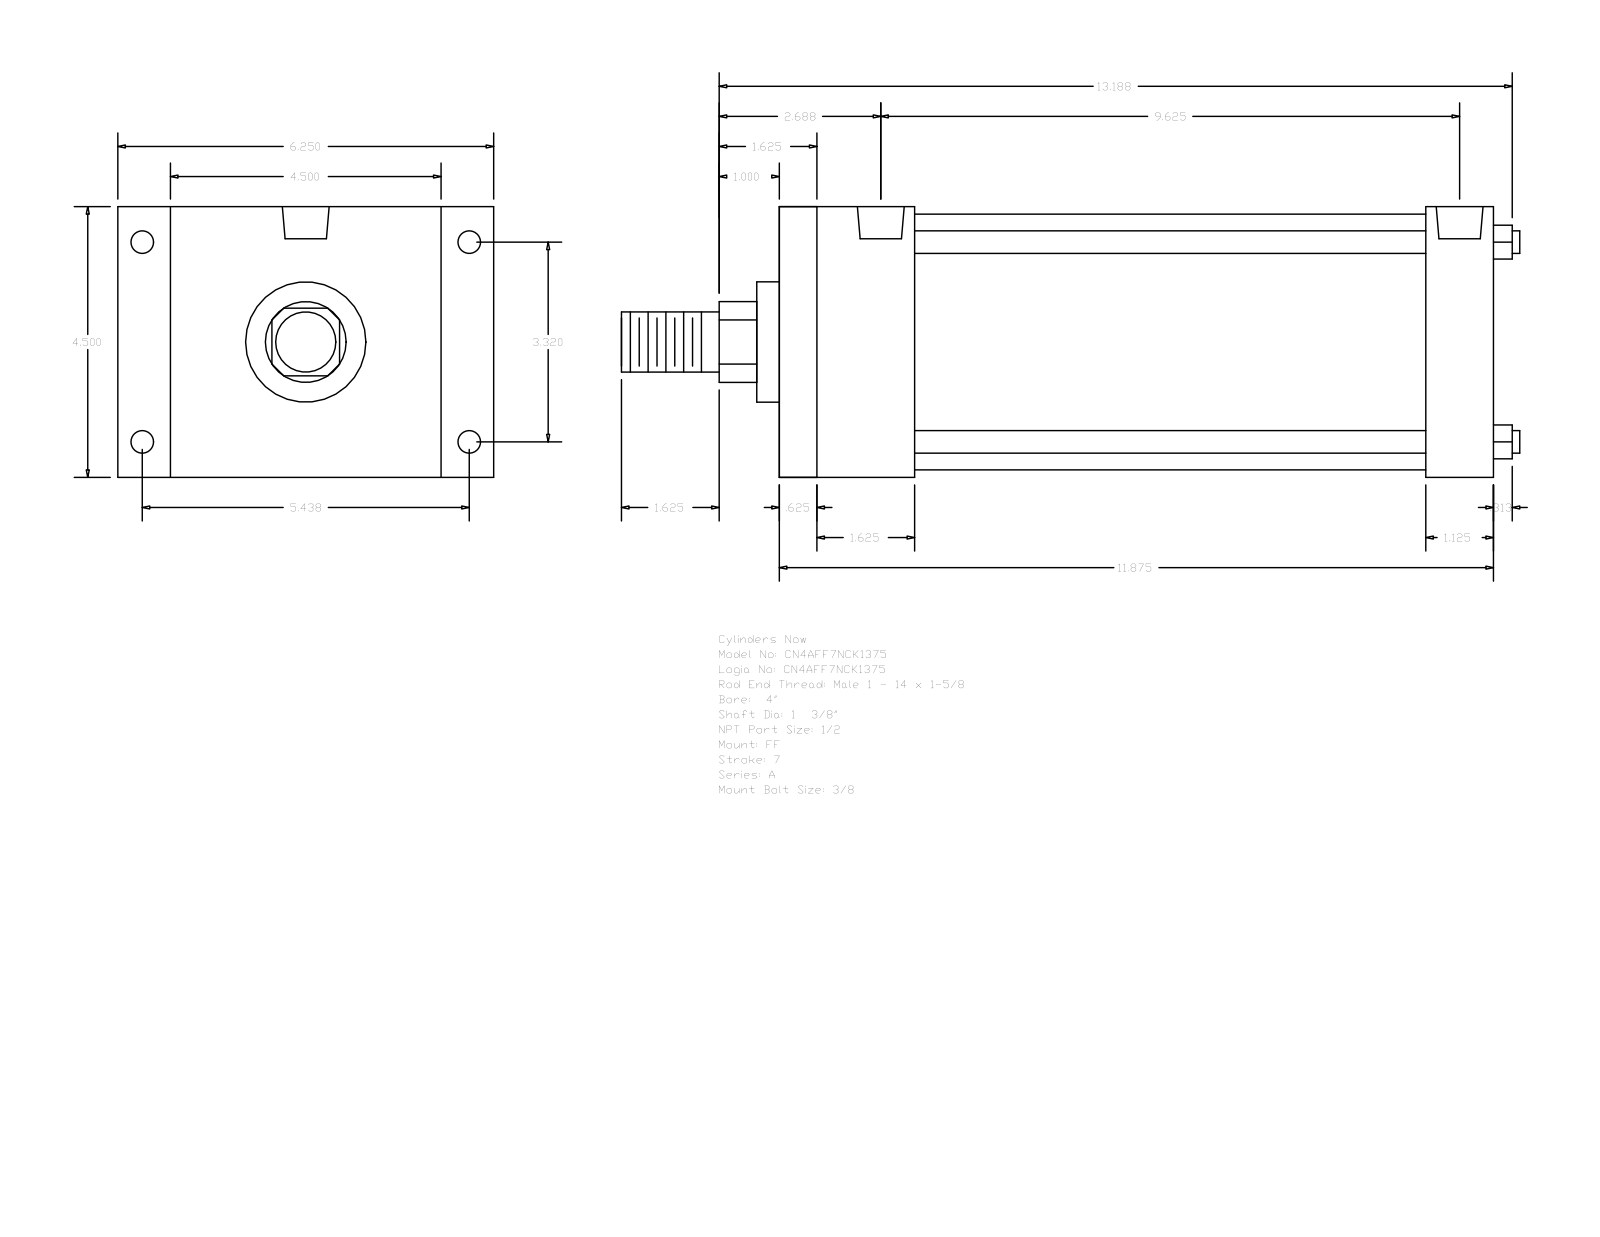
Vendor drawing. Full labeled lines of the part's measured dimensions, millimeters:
Part name (STEP PRODUCT): A_FF__0400_1.375
STEP written by: GSSL Pune (CONFIG_CONTROL_DESIGN)
Units: millimetres
Bodies: 0 solids, 92 faces (64 planar, 28 cylindrical, 0 other)
Overall size (bounding box): 379.41 × 158.75 × 114.3
Round holes (diameter × count): ⌀8.73 ×4, ⌀9.53 ×4, ⌀19.77 ×2
Round bosses / shafts (diameter × count): ⌀9.53 ×4, ⌀107.95 ×1, ⌀50.8 ×1, ⌀34.92 ×1, ⌀25.4 ×1
Partial cylindrical surfaces — rounded edges, fillets, slot ends (radius × count): R17.06 ×1
Main face-to-face distances: 114.3, 301.62, 285.75, 15.87, 57.15, 28.57, 22.23, 136.53, 273.05, 257.18
Hole centre spacings: 3.18, 84.32, 138.12, 161.82, 238.12, 241.3, 244.48
